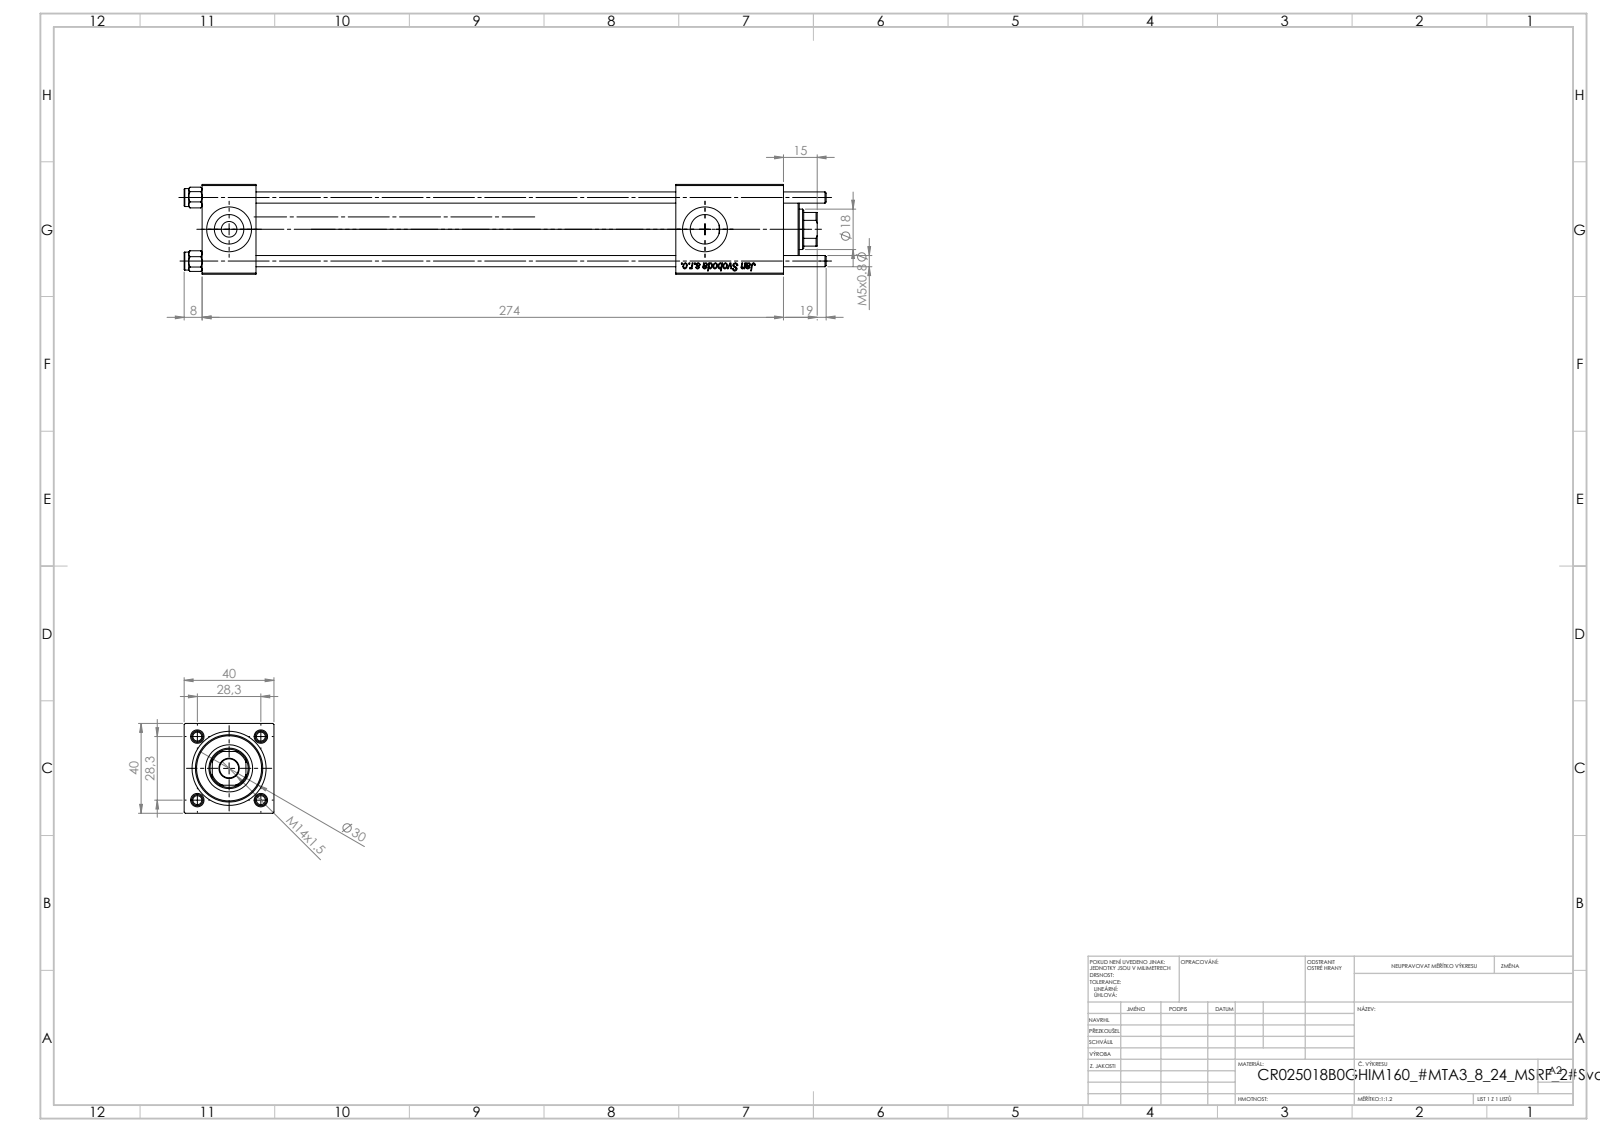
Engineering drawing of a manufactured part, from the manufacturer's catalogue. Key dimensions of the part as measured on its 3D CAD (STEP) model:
Part name (STEP PRODUCT): V215CR_VCP_B; V215_VC_A; V215CR_B_TYCINKA; NUT_M5_B (+1 more)
STEP written by: SolidWorks 2019 (CONFIG_CONTROL_DESIGN)
Units: millimetres
Bodies: 11 solids, 1152 faces (428 planar, 76 cylindrical, 648 other)
Overall size (bounding box): 286 × 40 × 40
Volume: 236 057 mm³ · Surface area: 102 238 mm²
Round holes (diameter × count): ⌀5 ×4, ⌀20 ×3, ⌀7 ×2, ⌀13.16 ×2, ⌀8.5 ×1, ⌀18 ×1, ⌀21 ×1, ⌀25 ×1, ⌀30 ×1
Round bosses / shafts (diameter × count): ⌀8 ×4, ⌀31 ×1
Partial cylindrical surfaces — rounded edges, fillets, slot ends (radius × count): R8.5 ×1
Main face-to-face distances: 40, 24, 211, 187, 230.3, 206.3, 19.3, 259, 235, 48
Hole centre spacings: 20.01, 28.3, 40.02, 212
